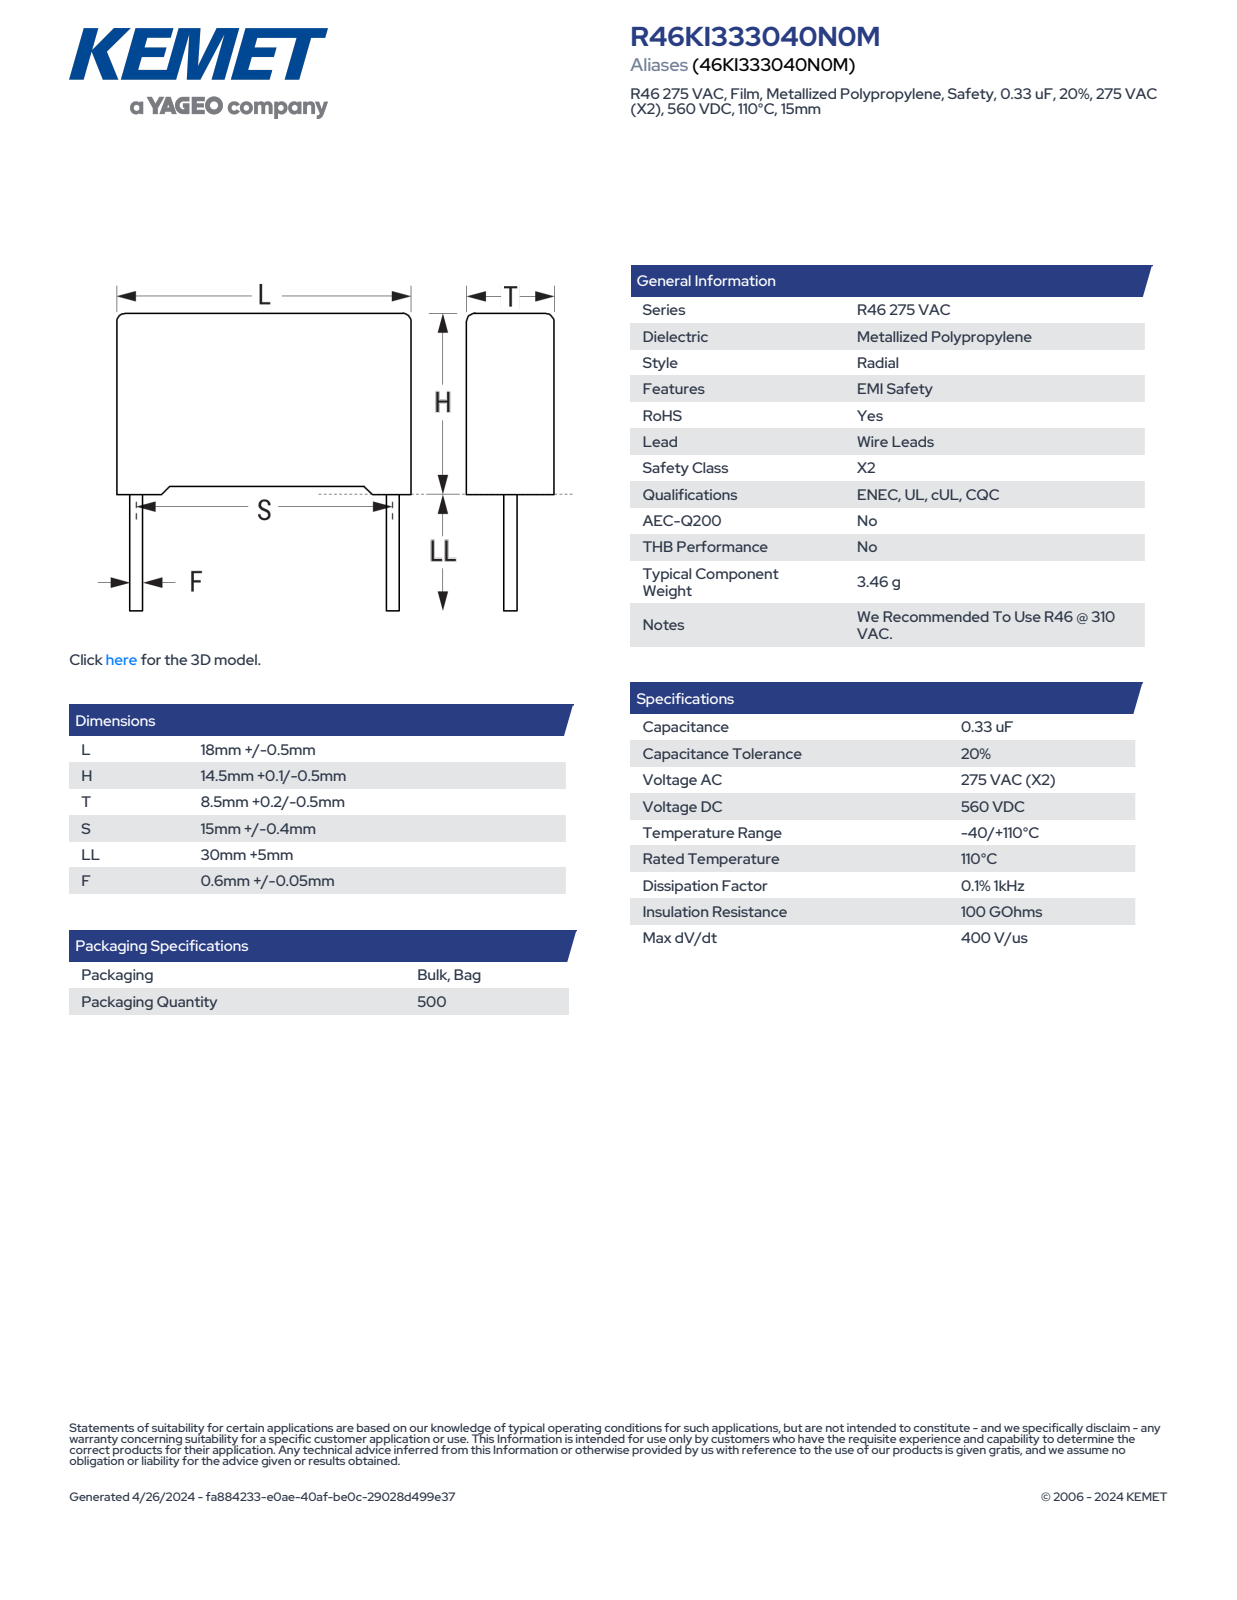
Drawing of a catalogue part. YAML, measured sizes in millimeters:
part_name: "CFR_RB2_18X14.5X8.5_L18.5H14.6T8.7S15LL35F0.65"
step_written_by: "SolidWorks 2021 (AUTOMOTIVE_DESIGN)"
units: millimeters
bodies: {solids: 4, faces: 85, planar: 77, cylindrical: 8, other: 0}
overall_size: [49.6, 18.5, 8.71]
volume: 2267
surface_area: 1291
round_bosses_or_shafts:
  - {diameter: 0.65, count: 2}
partial_cylinders:
  - {radius: 0.5, count: 4}
face_to_face_distances: [8.7, 13.85, 18.5, 0.62, 0.75, 14.6, 8.08, 0.5, 14.1, 17.88]
